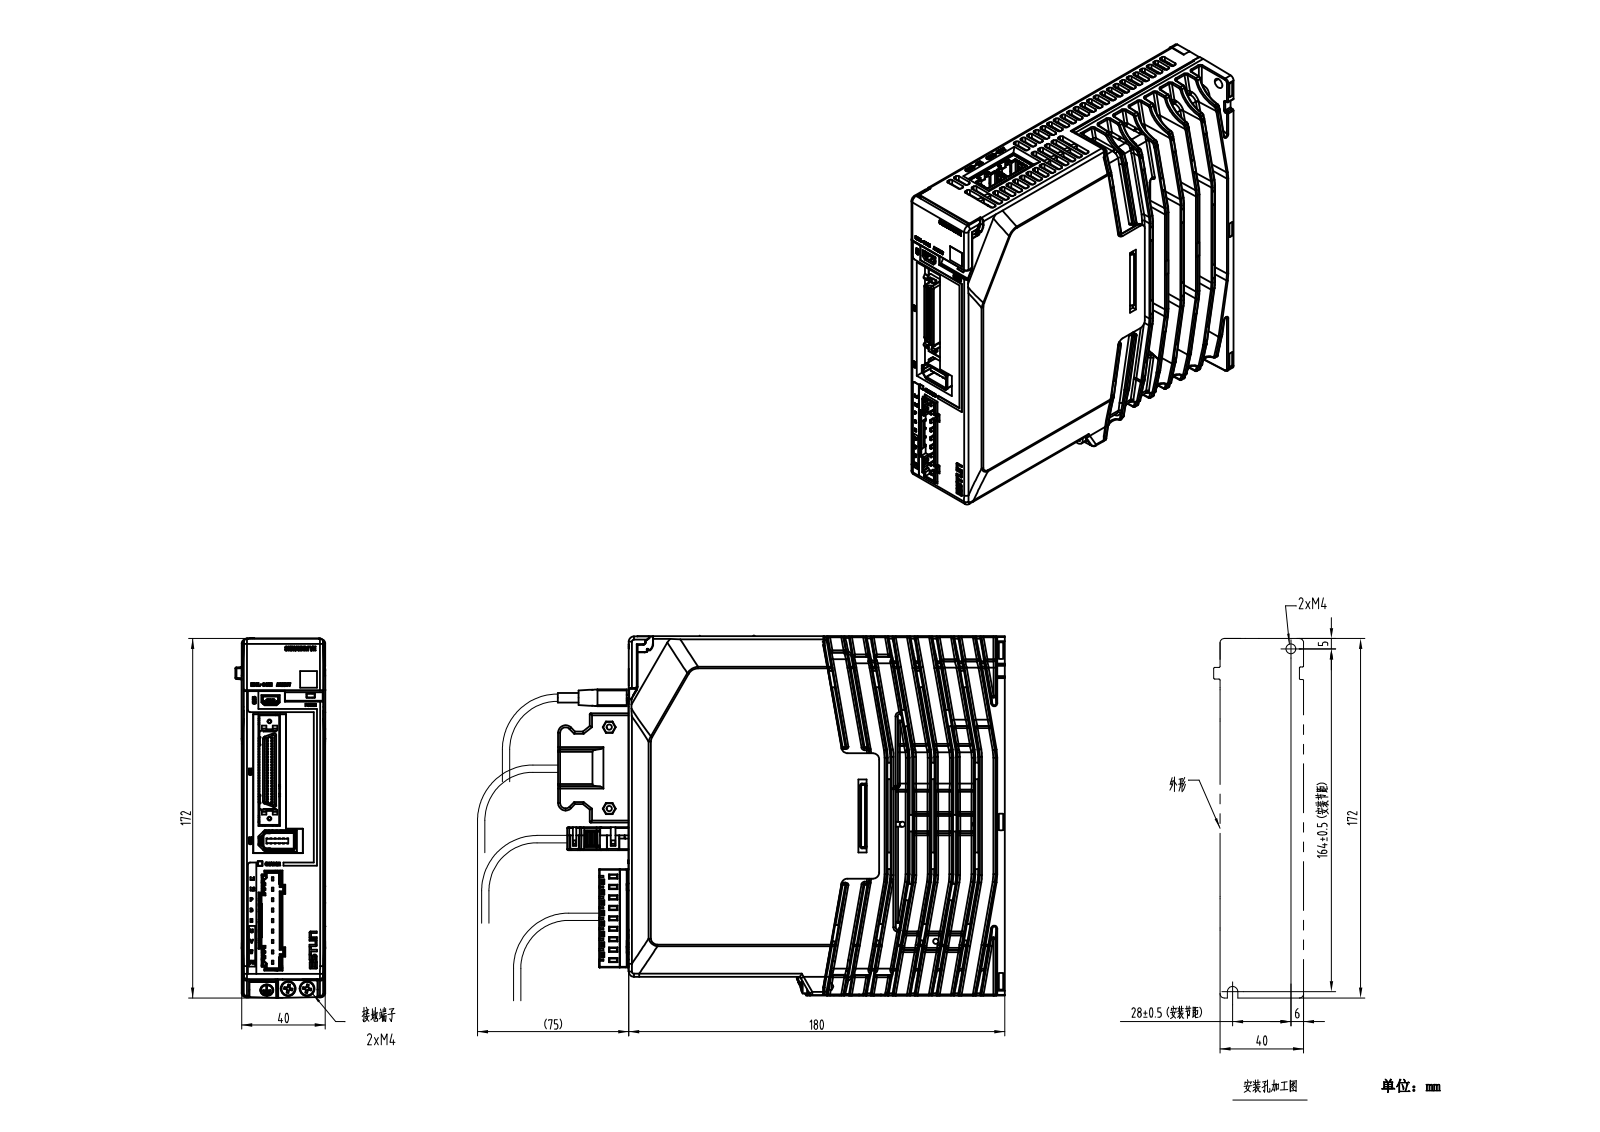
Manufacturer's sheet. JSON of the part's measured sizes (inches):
{"part_name": "ED3L-04AMA（安装外形图）", "step_written_by": "SolidWorks 2018 (CONFIG_CONTROL_DESIGN)", "units": "inches", "bodies": {"solids": 0, "faces": 3033, "planar": 1423, "cylindrical": 760, "other": 850}, "overall_size": [7.126, 6.78, 1.693], "round_holes": [[0.079, 2], [0.081, 2], [0.13, 2]], "round_bosses_or_shafts": [[0.018, 12], [0.286, 2], [0.268, 2], [0.265, 2], [0.22, 2], [0.276, 1], [0.118, 1], [0.079, 1]], "partial_cylinders_radius": [[0.02, 159], [0.039, 113], [0.012, 53], [0.008, 39], [0.059, 20], [0.035, 19], [0.157, 12], [0.118, 10]], "face_to_face_distances": [1.575, 0.407, 0.413, 0.079, 0.906, 1.567, 0.669, 0.827, 0.661, 0.813], "hole_center_spacings": [0.354, 1.831, 2.264, 3.222, 3.28, 5.046, 5.083]}
